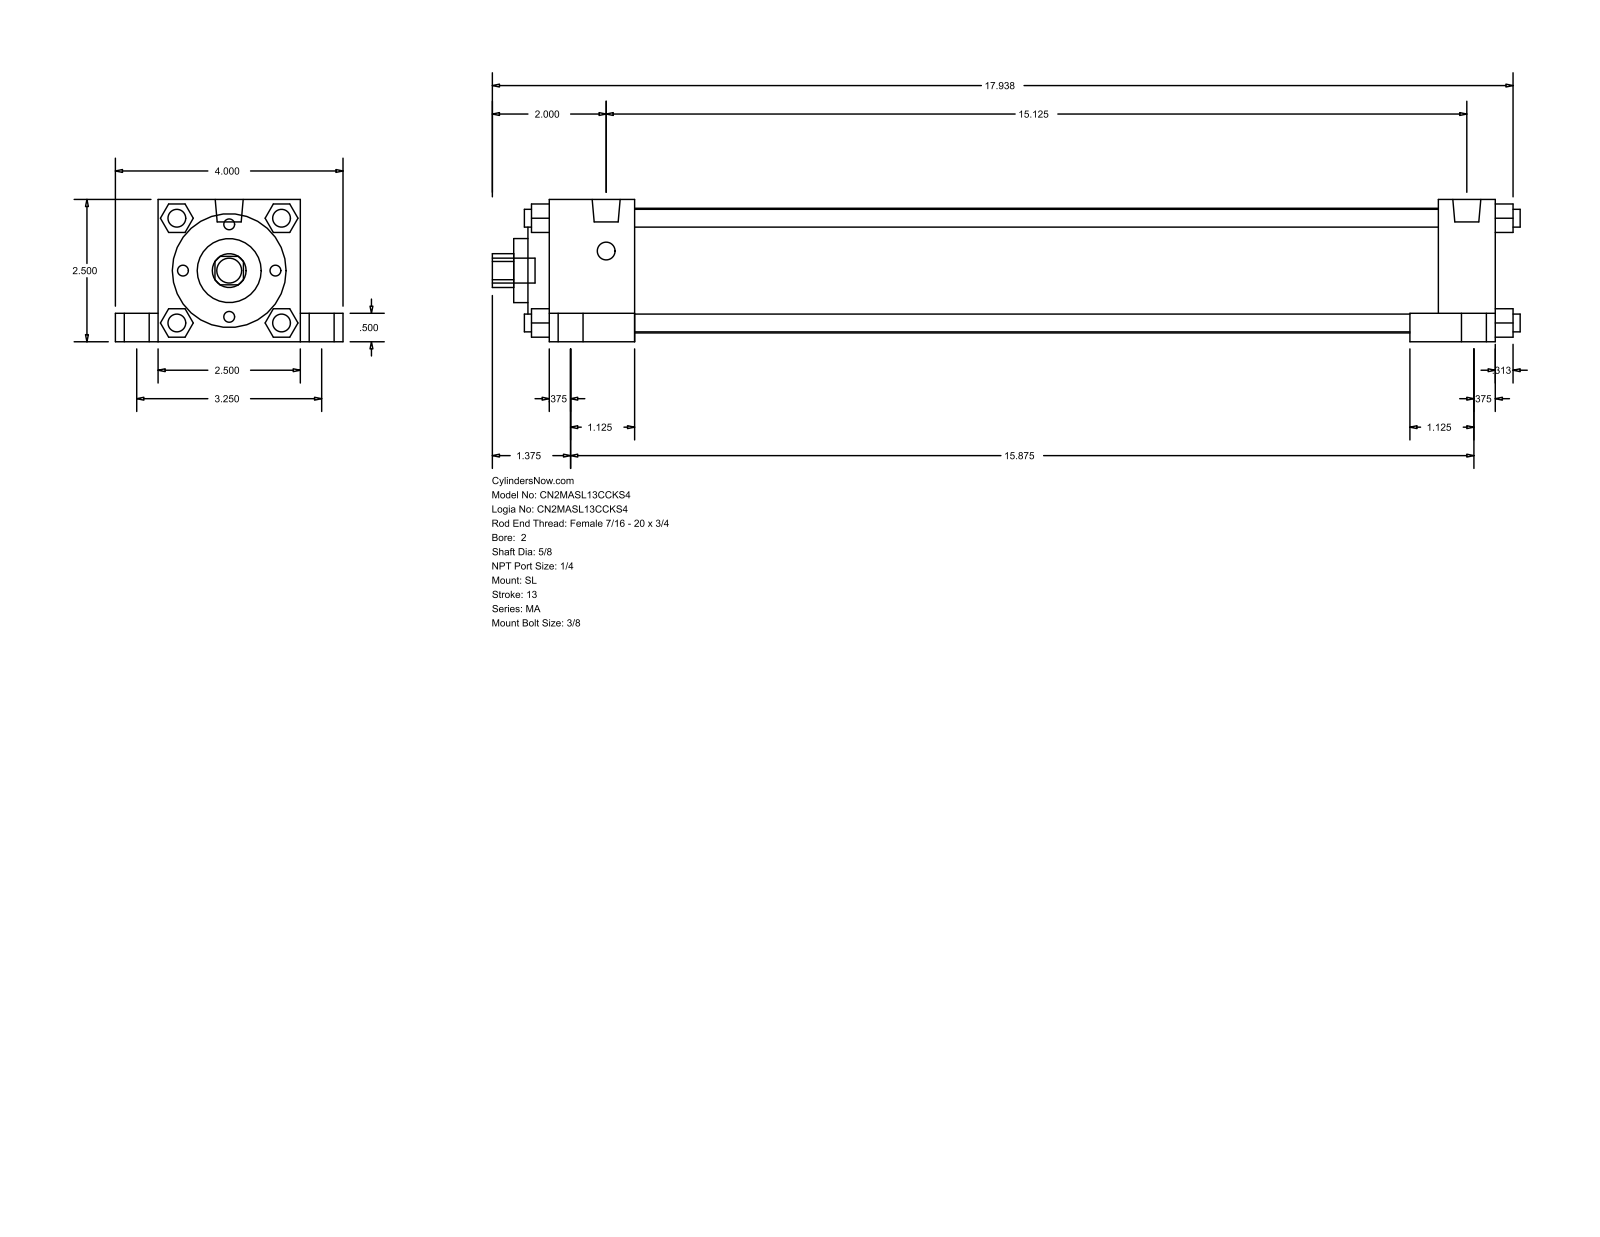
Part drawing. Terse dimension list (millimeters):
name: MA_SL__0200_0.625
written by: GSSL Pune (CONFIG_CONTROL_DESIGN)
unit: mm
bodies: 0 solids, 150 faces (113 planar, 37 cylindrical, 0 other)
size: 458.79 × 101.6 × 63.5
holes: 1× ⌀15.88, 1× ⌀28.57, 1× ⌀50.8, 1× ⌀55.63
bosses: 8× ⌀7.94, 5× ⌀11.11, 4× ⌀17.46, 2× ⌀12.49
rounds: 1× R7.54
face distances: 63.5, 12.7, 9.52, 358.77, 19.05, 82.55, 38.1, 50.8, 422.28, 384.18
